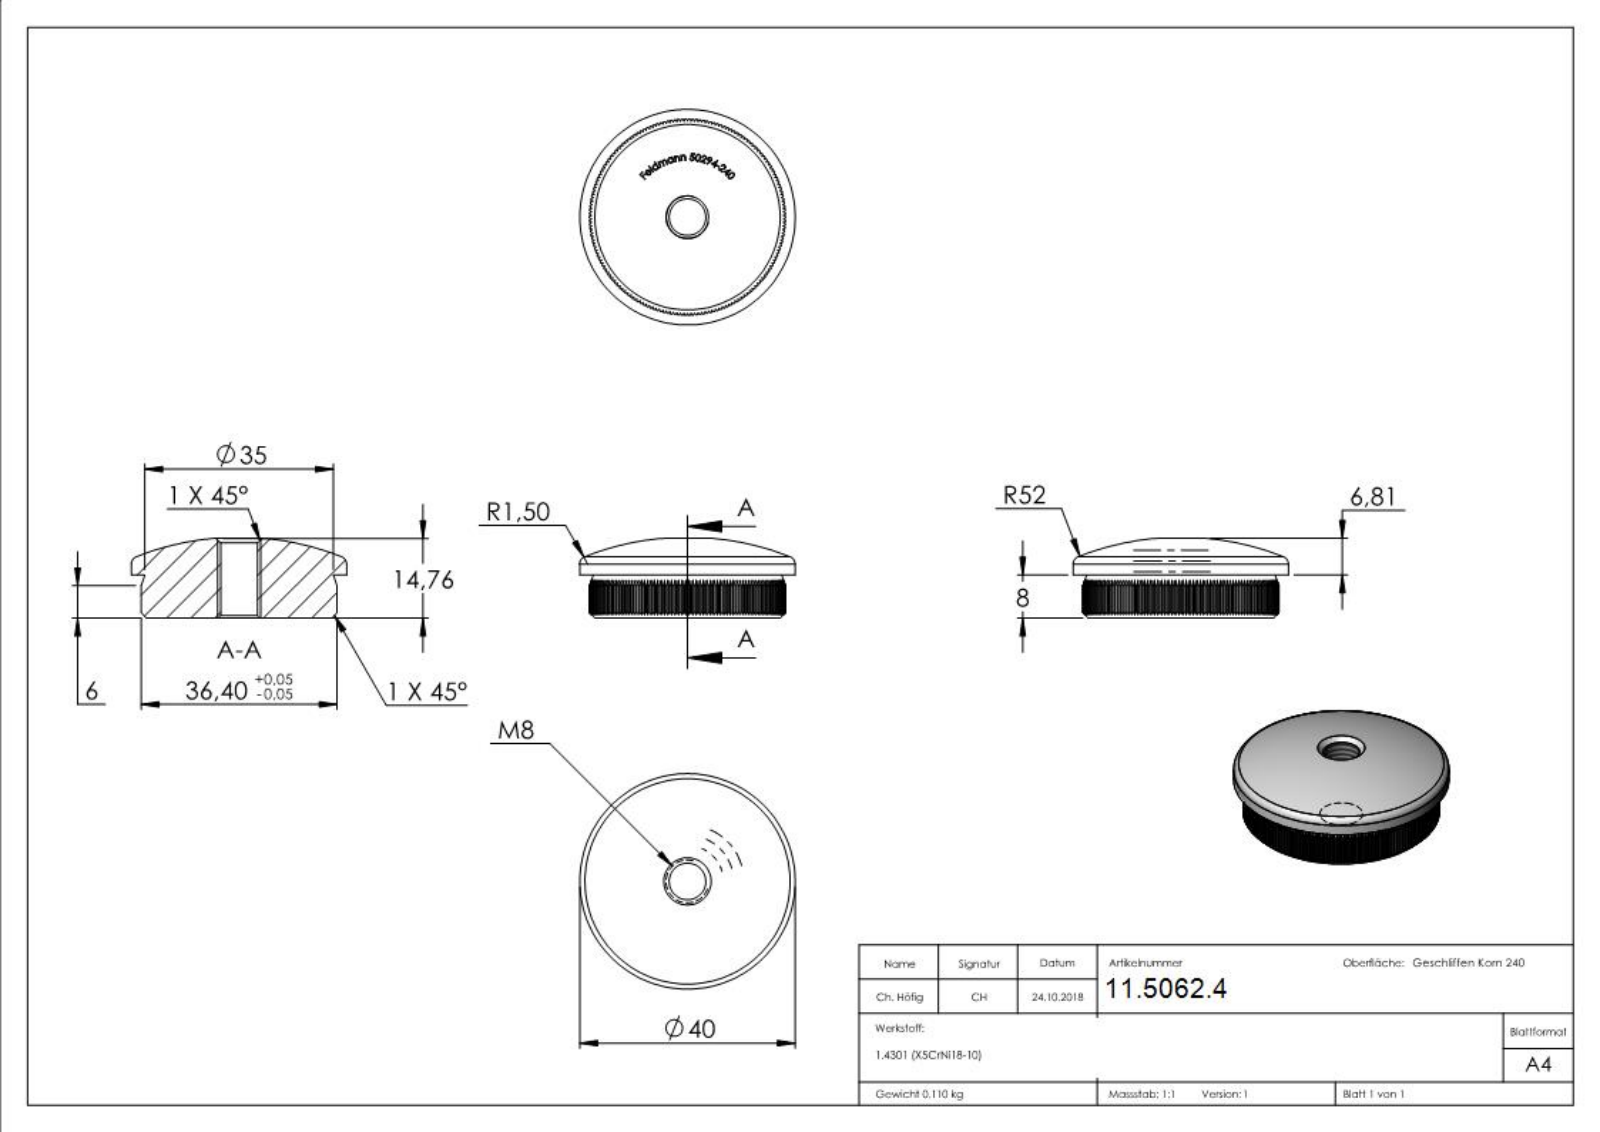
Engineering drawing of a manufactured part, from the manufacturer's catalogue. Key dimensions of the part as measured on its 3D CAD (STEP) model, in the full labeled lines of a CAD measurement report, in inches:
Part name (STEP PRODUCT): 50294-240
STEP written by: SolidWorks 2015 (CONFIG_CONTROL_DESIGN)
Units: inches
Bodies: 1 solid, 753 faces (472 planar, 174 cylindrical, 107 other)
Overall size (bounding box): 1.575 × 1.575 × 0.583
Volume: 0.846 in³ · Surface area: 6.916 in²
Round holes (diameter × count): ⌀0.268 ×1
Round bosses / shafts (diameter × count): ⌀1.575 ×1
Partial cylindrical surfaces — rounded edges, fillets, slot ends (radius × count): R0.717 ×1
Main face-to-face distances: 0.315, 0.703, 0.702, 0.704, 0.311, 0.026, 0.021, 0.026, 0.031, 0.028
